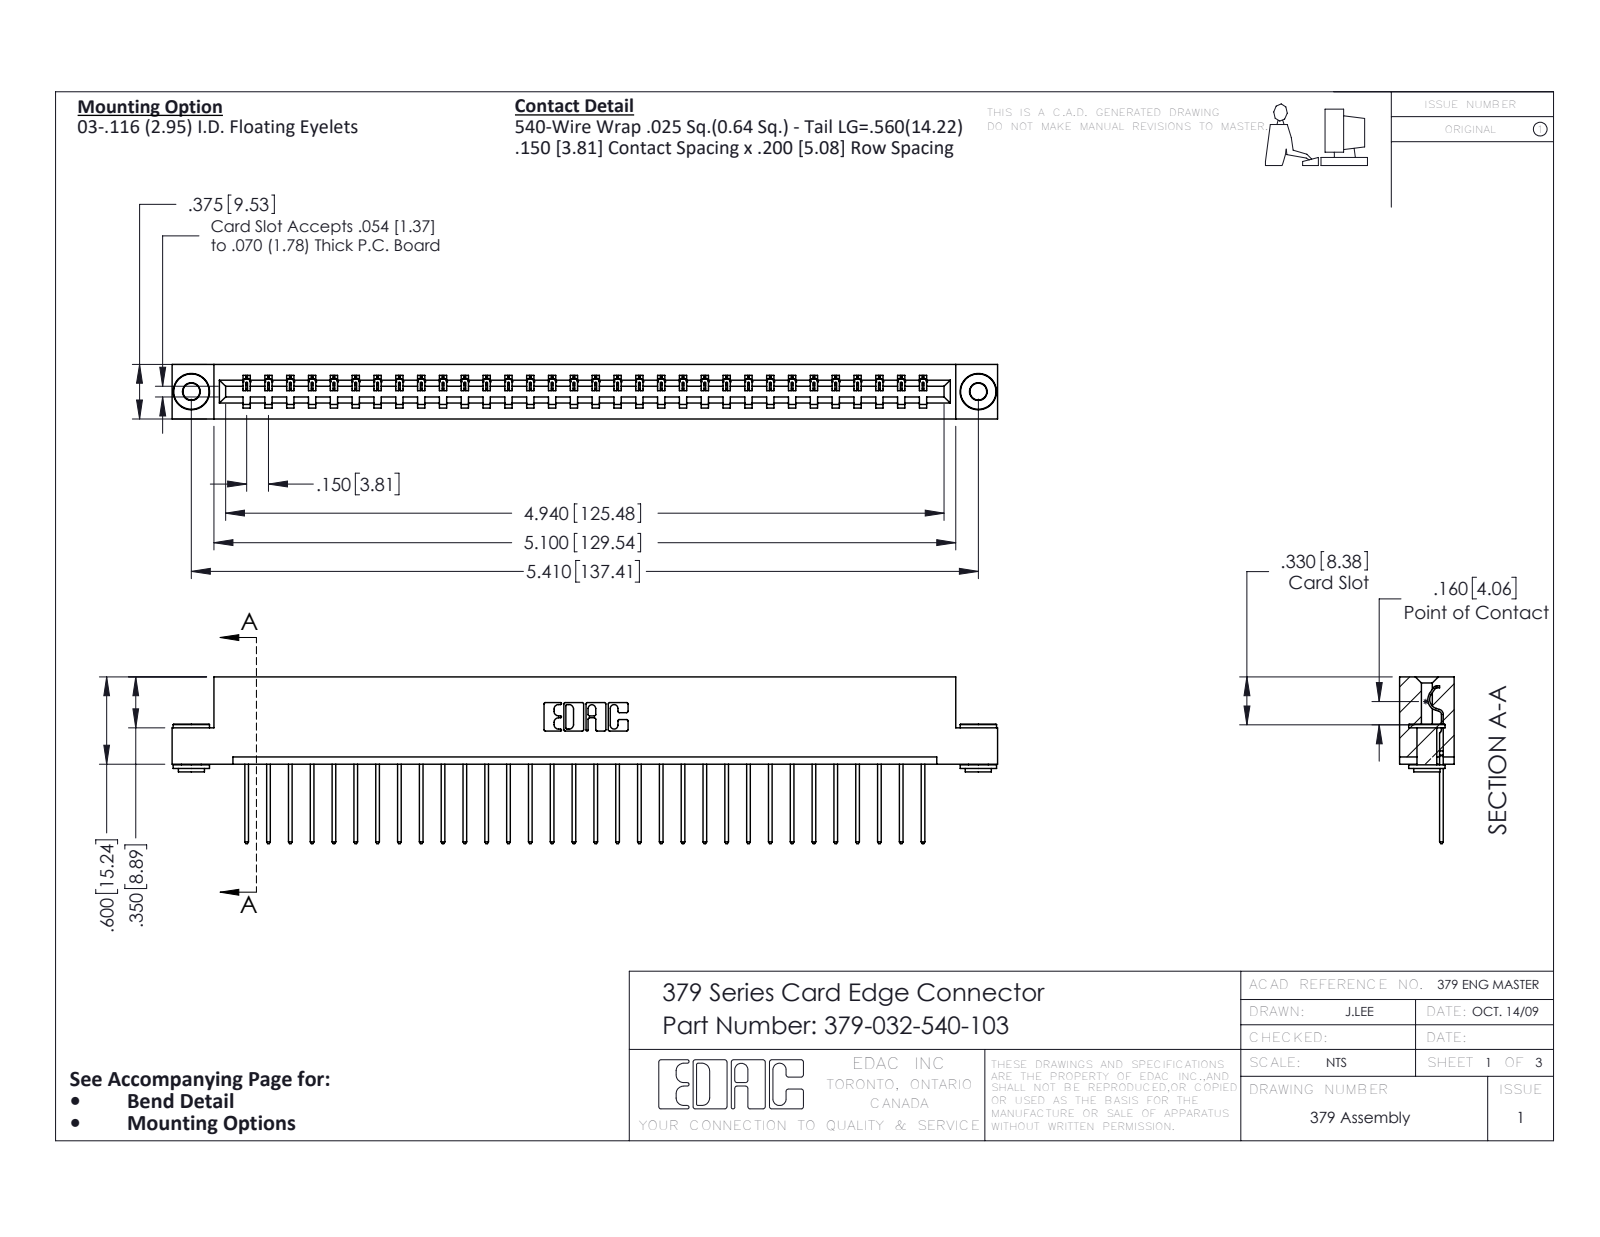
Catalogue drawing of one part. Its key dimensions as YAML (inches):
part_name: "379 Part_Flush - .156 Dia - TH; 379-032-540-103; 345-292-001_345-293-140; 345-250-002_345-250-002-102"
step_written_by: "SolidWorks 2016 (CONFIG_CONTROL_DESIGN)"
units: inches
bodies: {solids: 35, faces: 2008, planar: 1424, cylindrical: 576, other: 8}
overall_size: [5.675, 1.147, 0.375]
volume: 0.921
surface_area: 24.71
round_holes:
  - {diameter: 0.116, count: 2}
  - {diameter: 0.156, count: 2}
round_bosses_or_shafts:
  - {diameter: 0.25, count: 2}
  - {diameter: 0.18, count: 2}
  - {diameter: 0.136, count: 2}
partial_cylinders:
  - {radius: 0.006, count: 64}
  - {radius: 0.01, count: 64}
  - {radius: 0.01, count: 22}
  - {radius: 0.007, count: 6}
  - {radius: 0.031, count: 6}
  - {radius: 0.026, count: 3}
  - {radius: 0.014, count: 1}
  - {radius: 0.022, count: 1}
face_to_face_distances: [0.3, 0.075, 0.375, 0.225, 0.275, 0.2, 0.025, 0.1, 0.6, 0.55]
hole_center_spacings: [5.41]
